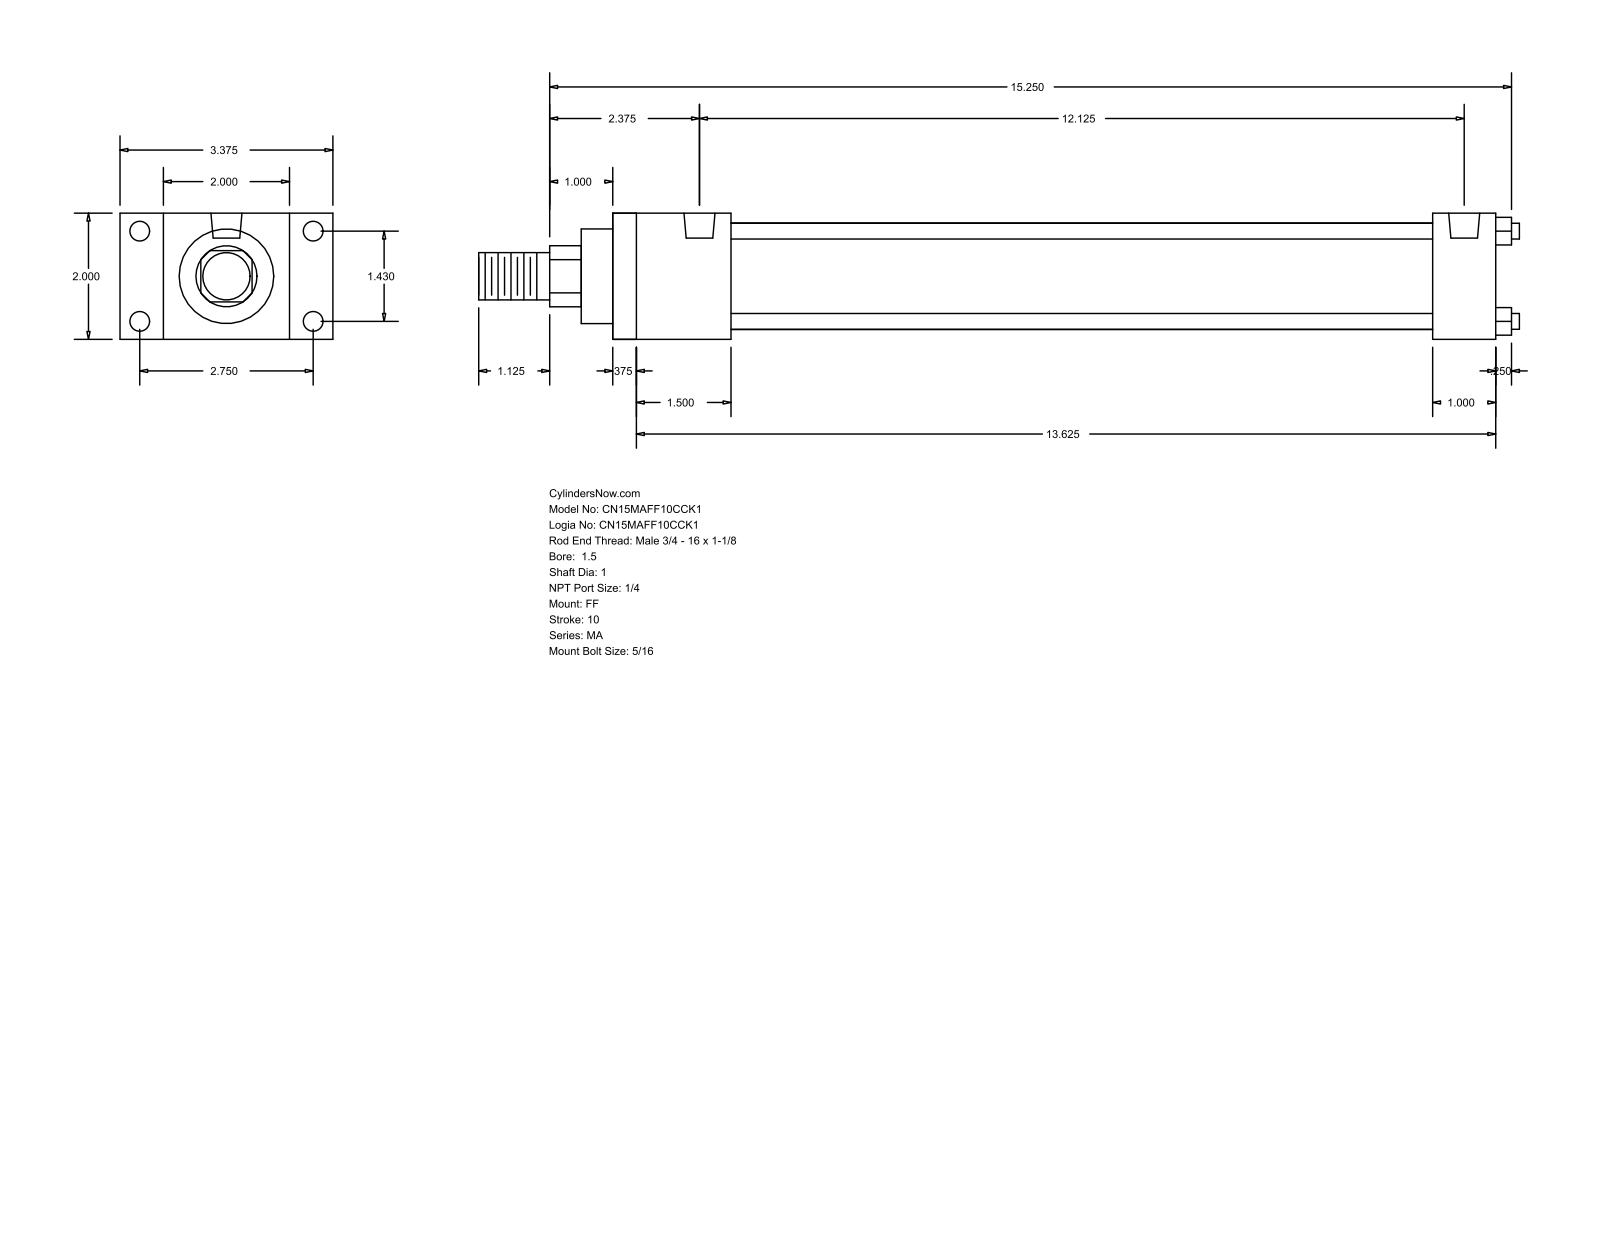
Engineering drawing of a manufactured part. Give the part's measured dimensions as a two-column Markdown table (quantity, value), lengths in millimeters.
| quantity | value |
| --- | --- |
| part name | MA_FF__0150_1 |
| STEP written by | GSSL Pune (CONFIG_CONTROL_DESIGN) |
| units | millimeters |
| bodies | 0 solids, 92 faces (64 planar, 28 cylindrical, 0 other) |
| overall size | 419.1 × 85.72 × 50.8 |
| round holes (diameter × count) | 7.94 × 8, 12.49 × 2 |
| round bosses / shafts (diameter × count) | 6.35 × 4, 42.93 × 1, 38.1 × 1, 25.4 × 1, 19.05 × 1 |
| partial cylindrical surfaces (radius × count) | 12.29 × 1 |
| main face-to-face distances | 50.8, 355.6, 9.52, 346.08, 25.4, 47.63, 330.2, 38.11, 320.68, 282.57 |
| hole center spacings | 36.32, 69.84, 78.72, 307.97 |
